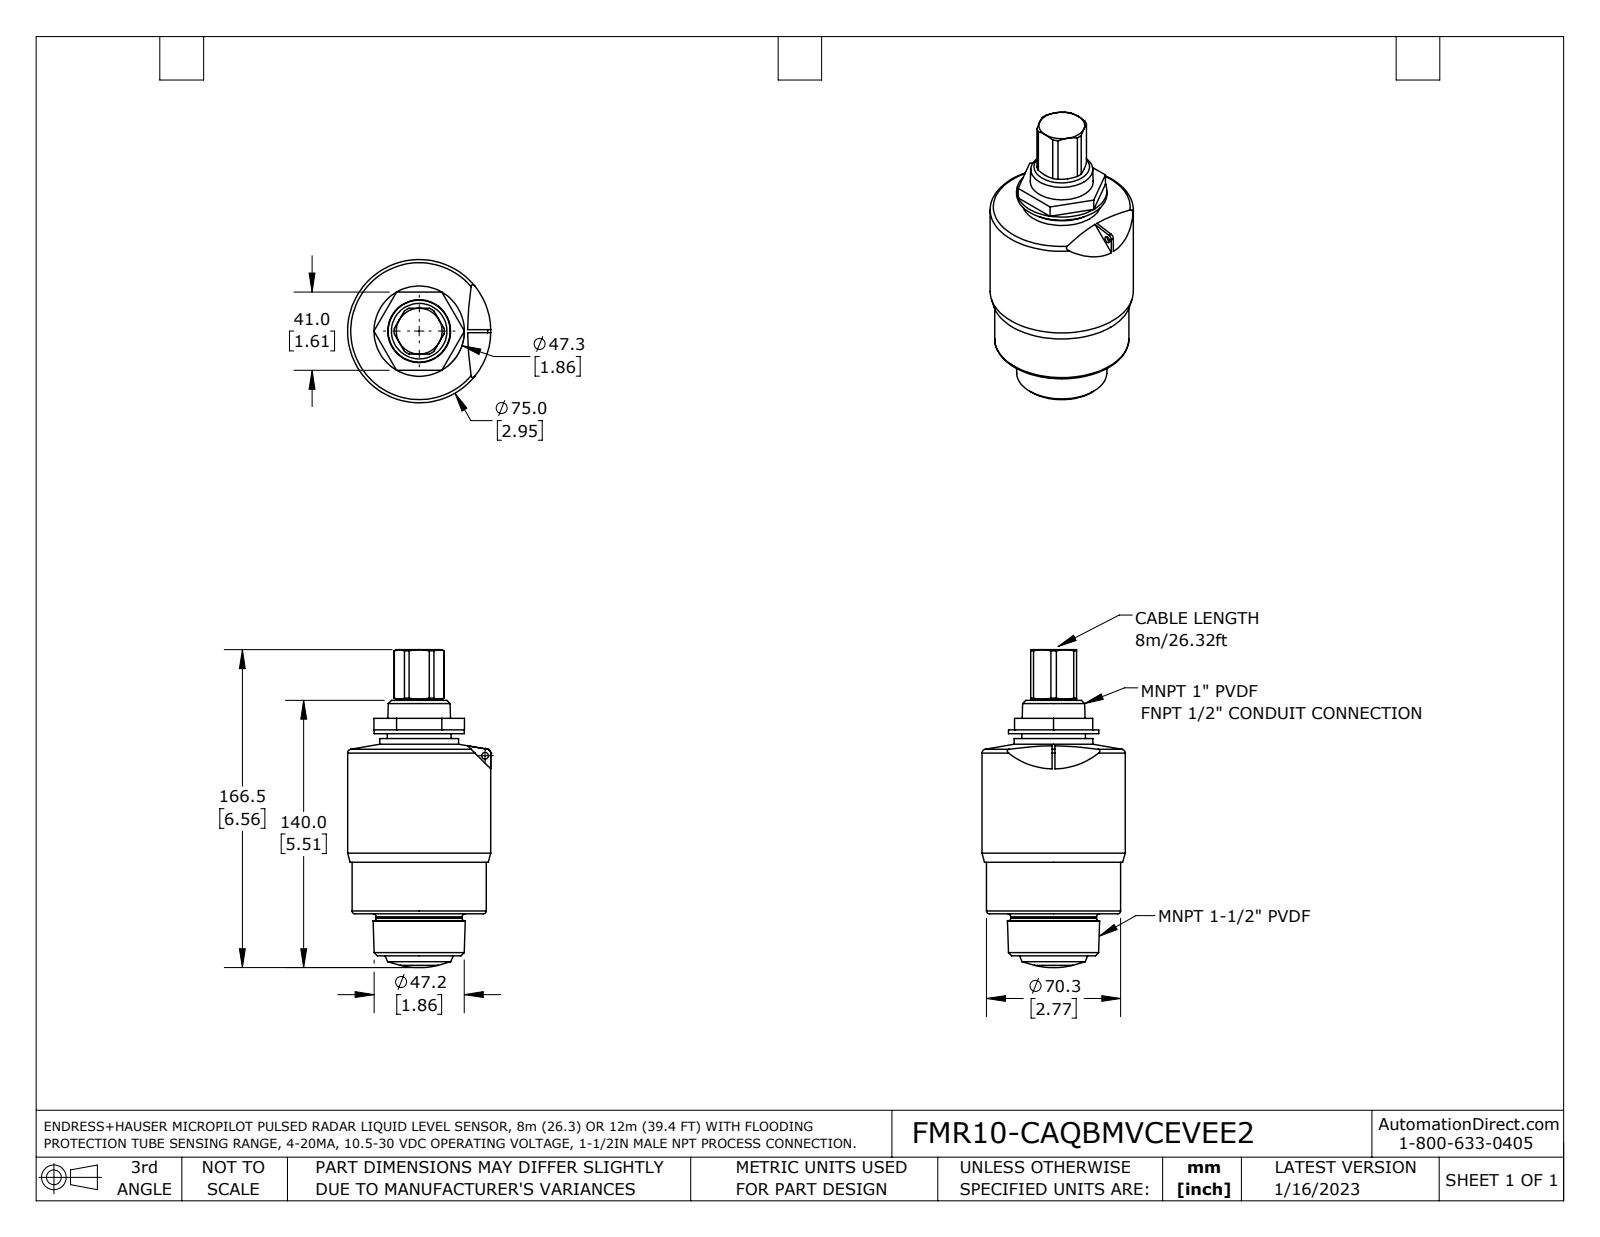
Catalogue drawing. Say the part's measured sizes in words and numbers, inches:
The part is named "FMR10-CAQBMVCEVEE2-Endress HauserConsultAG-3D-08-31-2022". Its 3-D file was written by "SolidWorks 2021 (AUTOMOTIVE_DESIGN)". It is 1 solid with 103 faces: 39 planar, 25 cylindrical and 39 other. Overall it measures 6.555 by 2.953 by 2.953 inches. Its volume is 27.59 cubic inches and its surface area 59.97 square inches. Round holes: 1 of diameter 0.138. Round bosses or shafts: 1 of diameter 2.953, 1 of diameter 2.768, 1 of diameter 1.9, 1 of diameter 1.862, 1 of diameter 1.772, 1 of diameter 1.626, 1 of diameter 1.315, 1 of diameter 0.697. Partial cylindrical surfaces (rounded edges, fillets, slot ends): 1 of radius 0.516. The main face-to-face distances are 3.713, 0.335, 1.28, 0.945, 4.028, 0.315, 0.866, 4.579, 4.894, 4.48.
